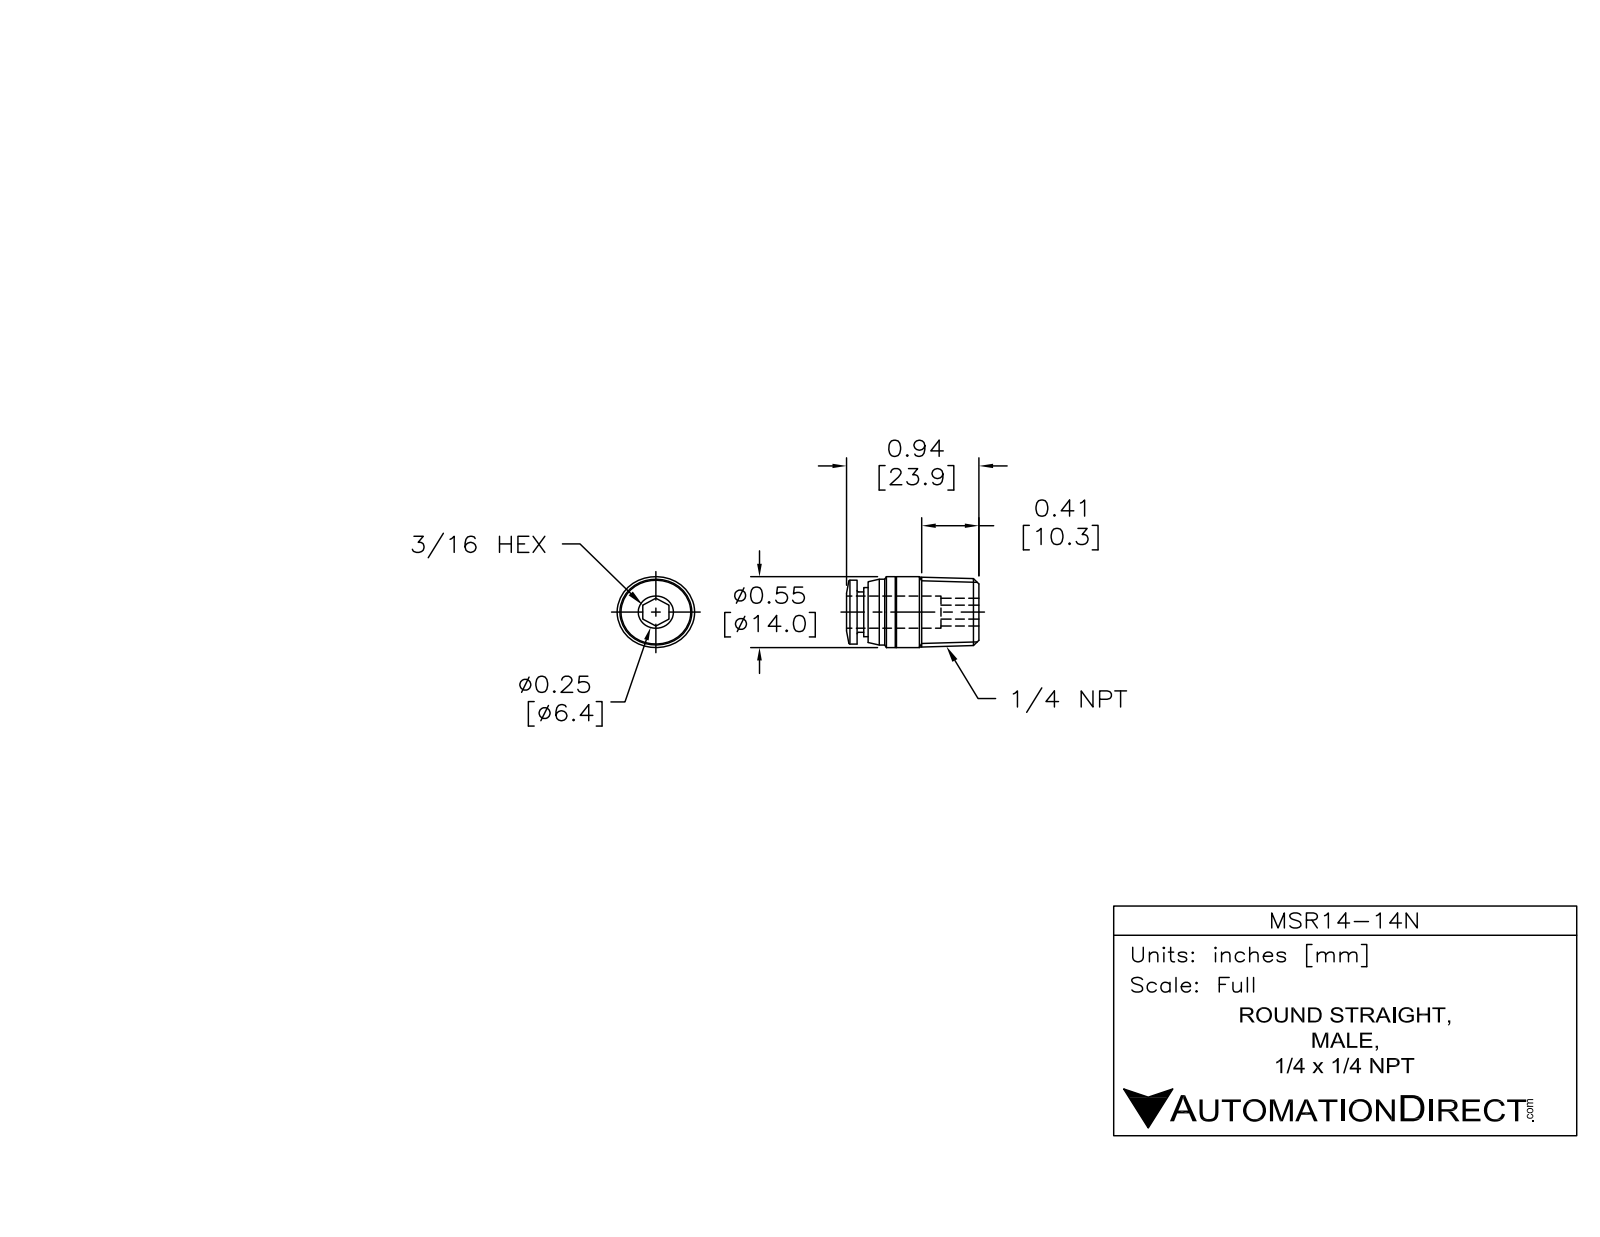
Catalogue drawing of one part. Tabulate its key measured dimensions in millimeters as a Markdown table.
| quantity | value |
| --- | --- |
| part name | MSR14-14N |
| STEP written by | SolidWorks 2015 (AUTOMOTIVE_DESIGN) |
| units | millimeters |
| bodies | 1 solid, 44 faces (6 planar, 16 cylindrical, 22 other) |
| overall size | 23.9 × 14 × 14 |
| volume | 2 490 mm³ |
| surface area | 1 772 mm² |
| round holes (diameter × count) | 4.8 × 1, 6.6 × 1 |
| round bosses / shafts (diameter × count) | 14 × 1, 13 × 1, 12.6 × 1, 9.7 × 1, 8 × 1 |
| main face-to-face distances | 22, 20, 2, 20.8, 0.8, 1.2, 7, 13, 13.8, 15 |
